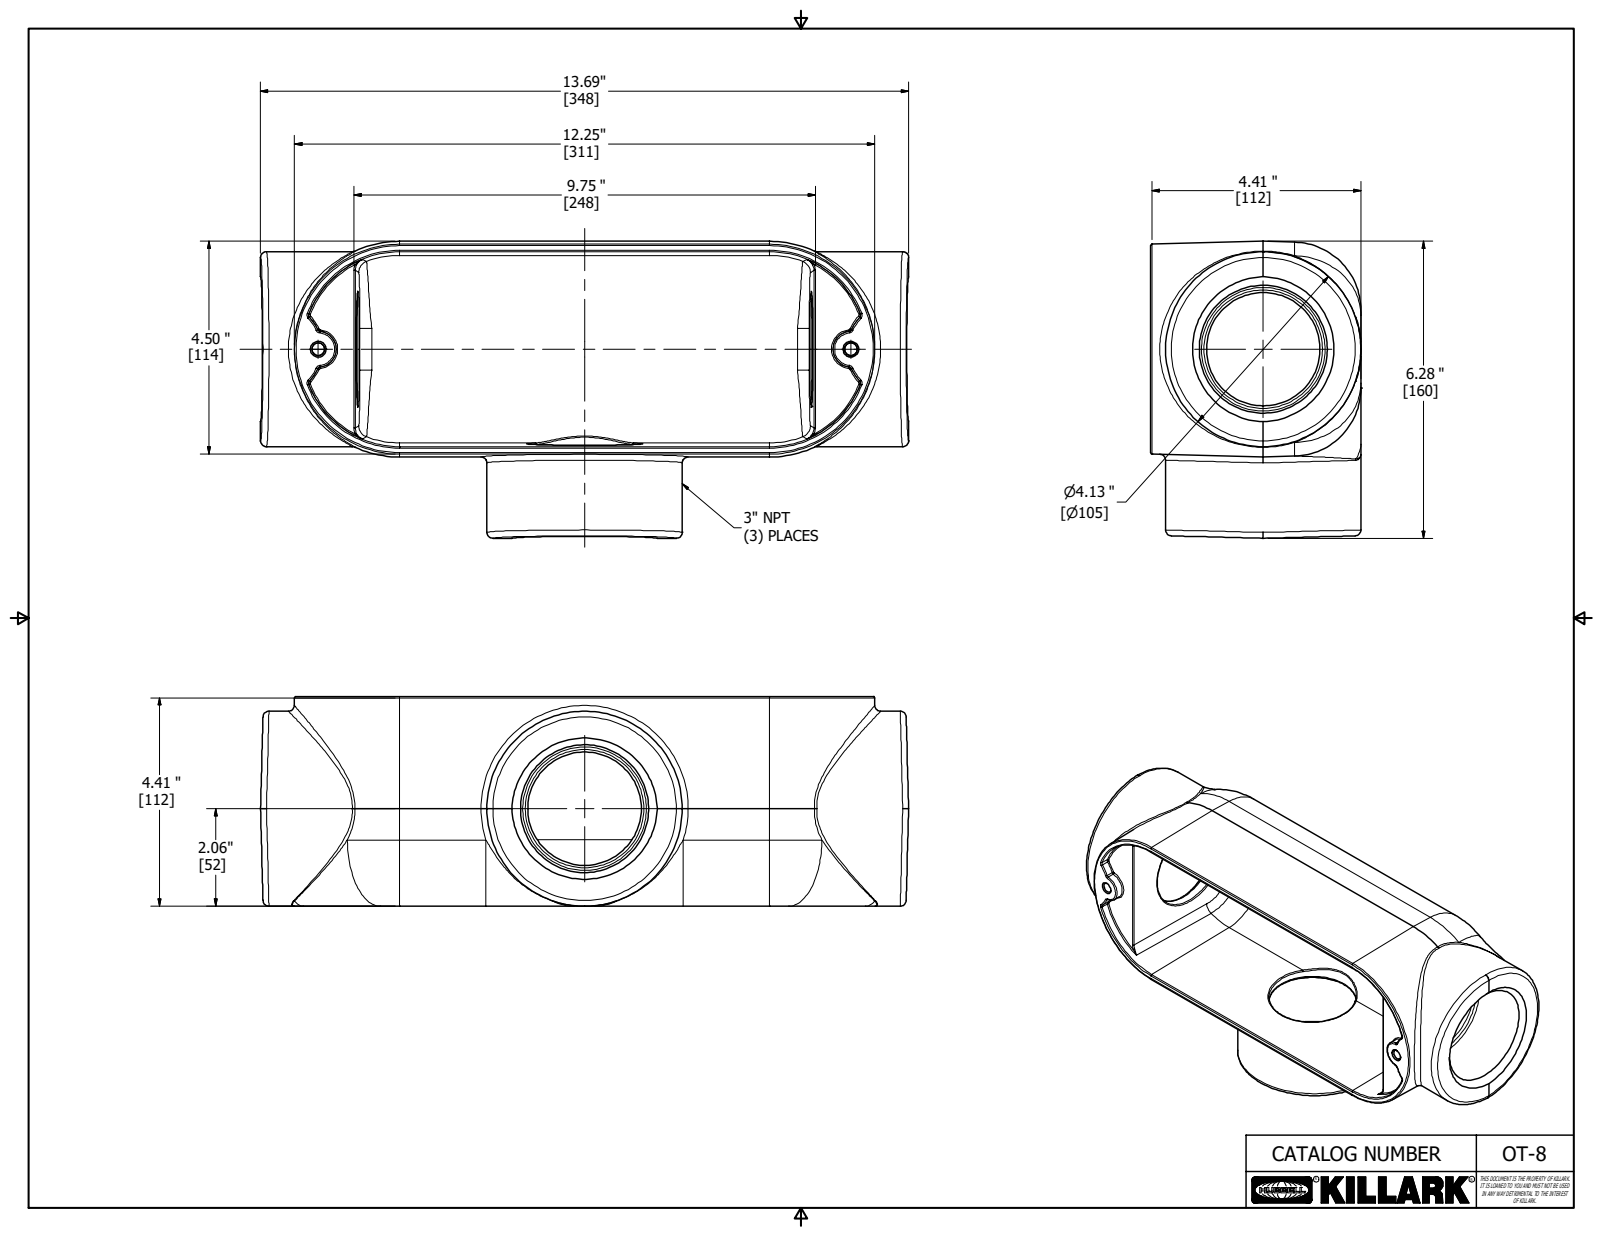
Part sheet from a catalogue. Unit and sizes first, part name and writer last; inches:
Units: inches
Overall size (bounding box): 13.688 × 6.281 × 4.438
Round holes (diameter × count): ⌀2.396 ×2, ⌀0.502 ×1
Round bosses / shafts (diameter × count): ⌀4.125 ×2, ⌀0.752 ×1
Partial cylindrical surfaces — rounded edges, fillets, slot ends (radius × count): R0.031 ×28, R0.03 ×2, R0.25 ×2, R1.25 ×2, R1.437 ×2, R0.031 ×1, R0.063 ×1, R0.171 ×1
Main face-to-face distances: 4.281, 0.187, 0.28, 4.561, 0.031, 0.219, 2.055, 6.281, 13.687, 11.632
Volume: 75.47 in³ · Surface area: 385.2 in²
Bodies: 1 solid, 2069 faces (1058 planar, 73 cylindrical, 938 other)
Part name (STEP PRODUCT): 12358-1
STEP written by: Autodesk Inventor 2018 (AUTOMOTIVE_DESIGN)
